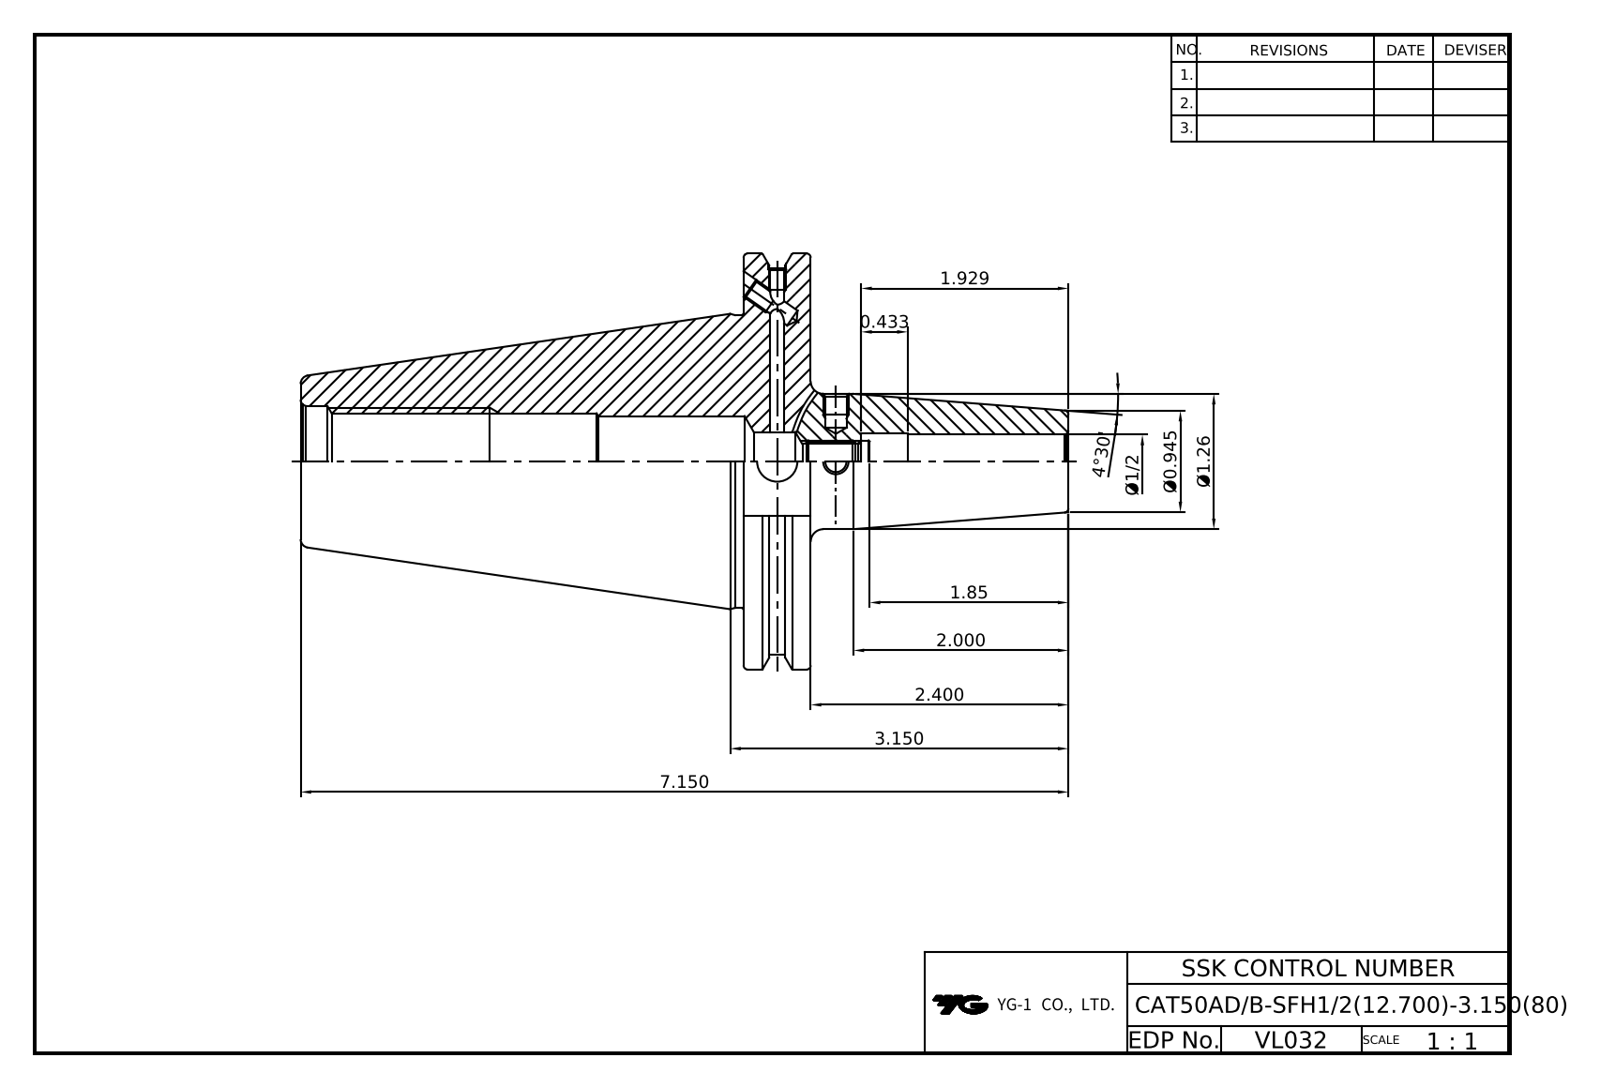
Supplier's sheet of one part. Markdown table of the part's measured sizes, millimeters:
| quantity | value |
| --- | --- |
| part name | LO-CAT50ADB-SFH12.7-80 |
| STEP written by | Autodesk Inventor 2025 (AUTOMOTIVE_DESIGN) |
| units | millimeters |
| bodies | 1 solid, 86 faces (37 planar, 27 cylindrical, 22 other) |
| overall size | 181.6 × 98.42 × 94.69 |
| volume | 353 942 mm³ |
| surface area | 52 208 mm² |
| round holes (diameter × count) | 3.24 × 2, 4.13 × 2, 4.2 × 2, 5 × 2, 8.92 × 1, 9.53 × 1, 12.7 × 1, 13.9 × 1, 14 × 1, 21.97 × 1, 26.2 × 1 |
| round bosses / shafts (diameter × count) | 98.42 × 1, 91.29 × 1, 69.25 × 1, 32 × 1 |
| main face-to-face distances | 15.88, 104.77, 120.65, 73.03, 25.9, 181.6, 76.83, 60.95, 110.82, 6.05 |
